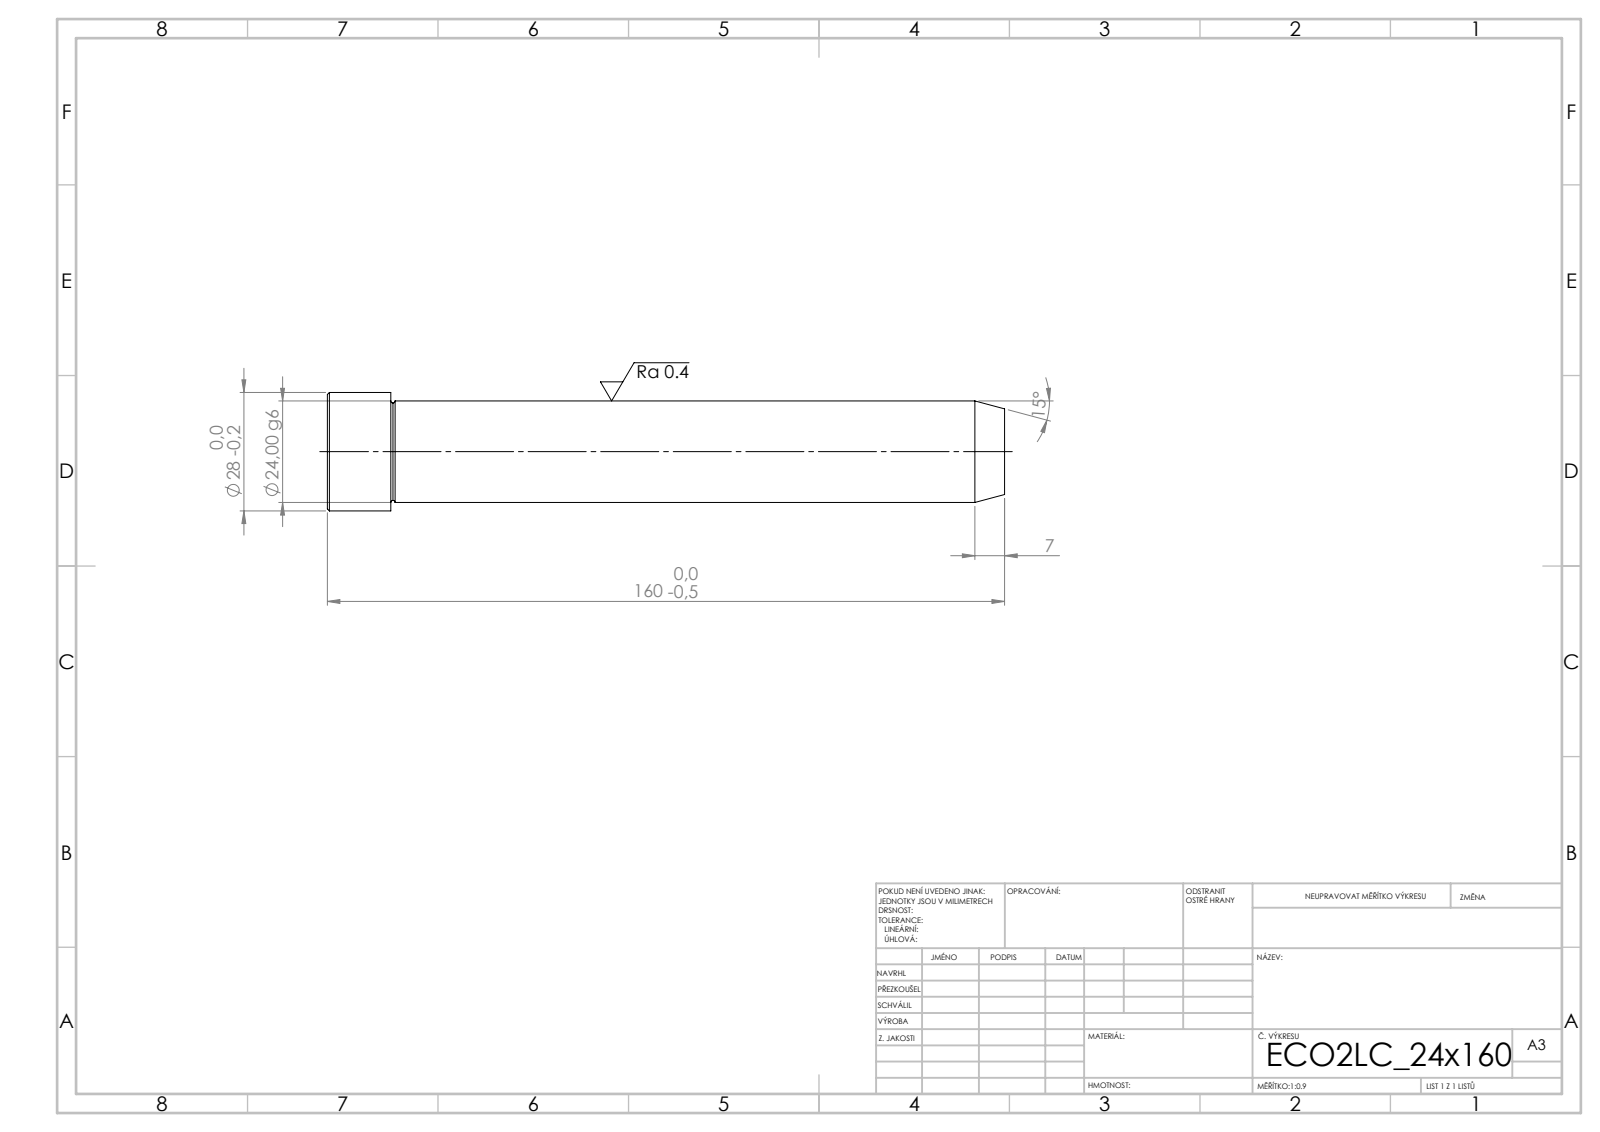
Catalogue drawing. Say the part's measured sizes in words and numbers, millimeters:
Its 3-D file was written by "SolidWorks 2019 (CONFIG_CONTROL_DESIGN)". It is 1 solid with 15 faces: 3 planar, 4 cylindrical and 8 other. Overall it measures 160 by 28 by 28 millimeters. Its volume is 74 324 cubic millimeters and its surface area 13 343 square millimeters. Round bosses or shafts: 1 of diameter 28, 1 of diameter 24. The main face-to-face distances are 160, 145, 15.
